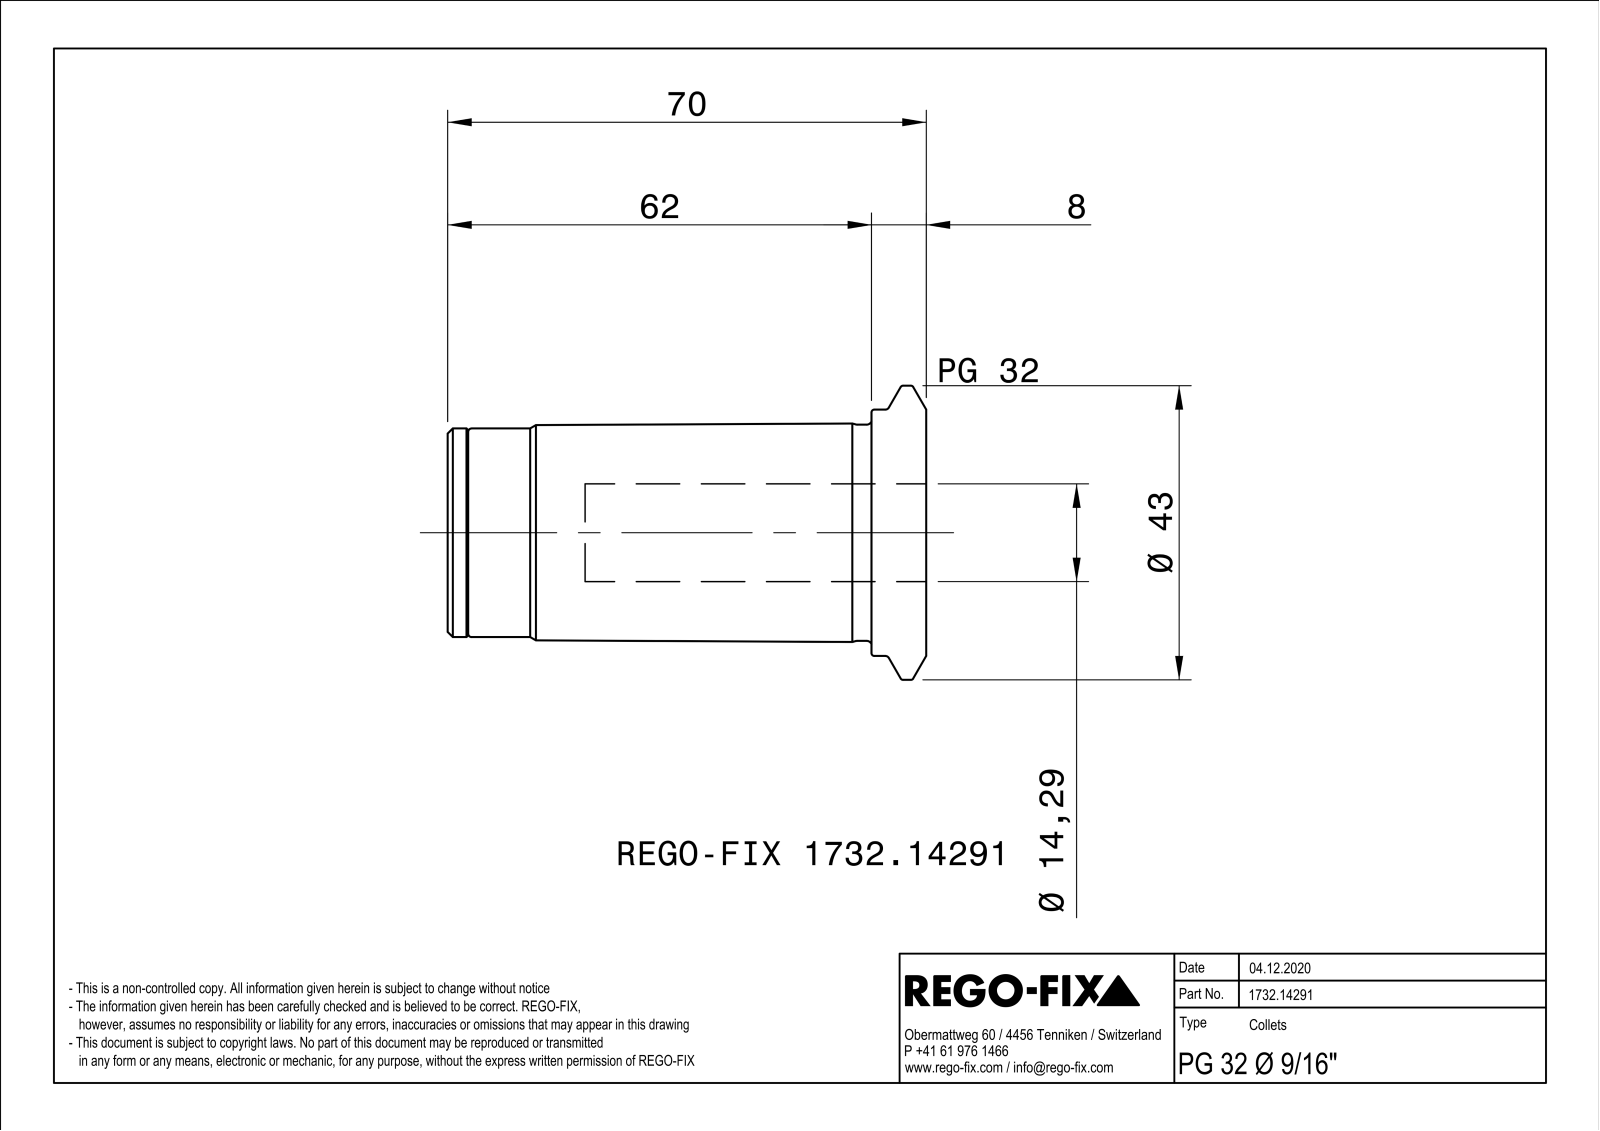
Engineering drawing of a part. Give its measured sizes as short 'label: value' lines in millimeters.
name: NOCUT
written by: SIEMENS PLM Software Solid Edge ST10 (AUTOMOTIVE_DESIGN)
unit: mm
bodies: 1 solid, 127 faces (31 planar, 41 cylindrical, 55 other)
size: 70 × 43 × 42.99
volume: 43 626 mm³; area: 16 557 mm²
holes: 3× ⌀4, 1× ⌀8.92, 1× ⌀10.5, 1× ⌀14.29, 1× ⌀15.5, 1× ⌀26.92, 1× ⌀28.5
bosses: 1× ⌀43, 1× ⌀36, 1× ⌀31.6, 1× ⌀30.5, 1× ⌀26.5, 1× ⌀21
rounds: 6× R2, 3× R3.5, 1× R3.98, 1× R4.75, 1× R8.75
face distances: 1, 70, 58, 12, 59, 11, 8, 60, 2, 10
hole spacings: 7.75, 13.42, 13.43
